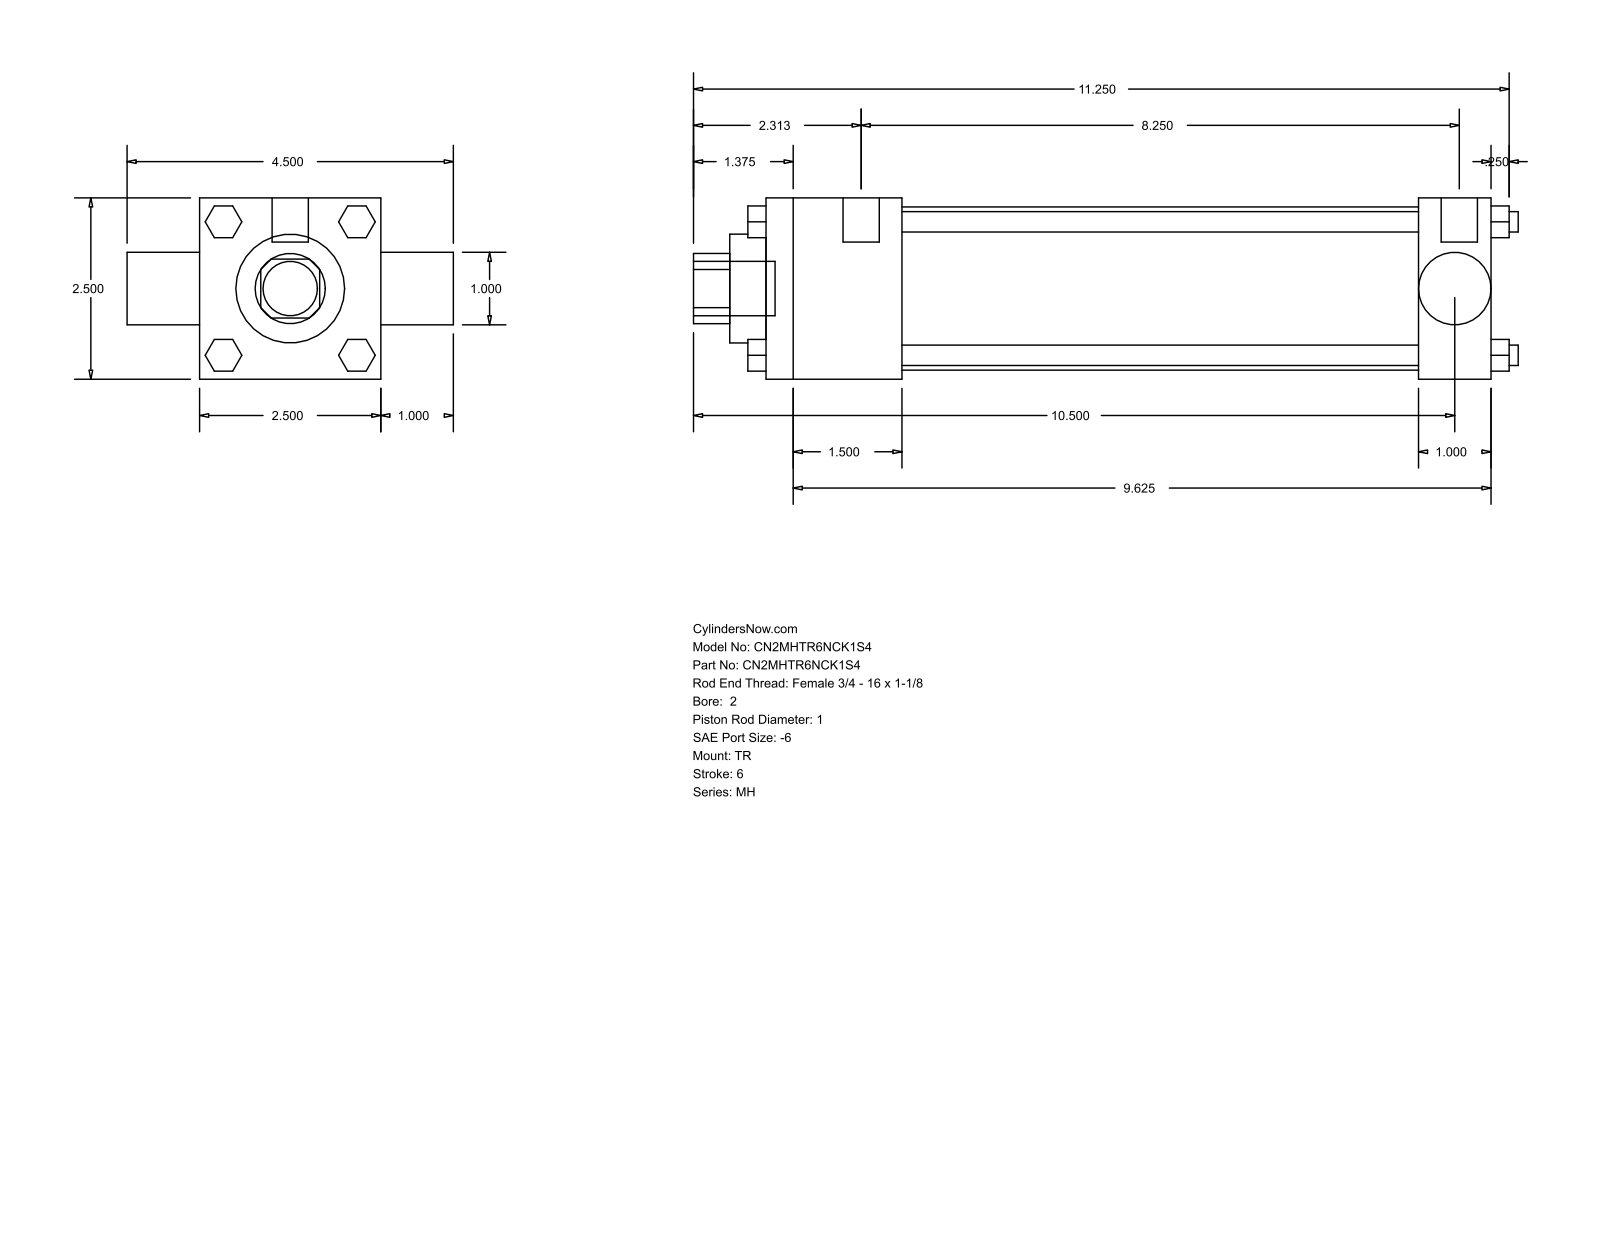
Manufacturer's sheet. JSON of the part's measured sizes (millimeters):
{"part_name": "MH_TR__0200_1", "step_written_by": "GSSL Pune (CONFIG_CONTROL_DESIGN)", "units": "millimeters", "bodies": {"solids": 0, "faces": 120, "planar": 92, "cylindrical": 28, "other": 0}, "overall_size": [288.93, 114.3, 63.5], "round_holes": [[25.35, 1], [25.4, 1], [38.1, 1], [57.15, 1]], "round_bosses_or_shafts": [[7.14, 4], [5.56, 3], [12.7, 2], [19.05, 1]], "partial_cylinders_radius": [[12.29, 1]], "face_to_face_distances": [63.5, 254, 25.4, 47.63, 228.6, 180.97, 206.37, 88.9, 266.7, 6.35]}
